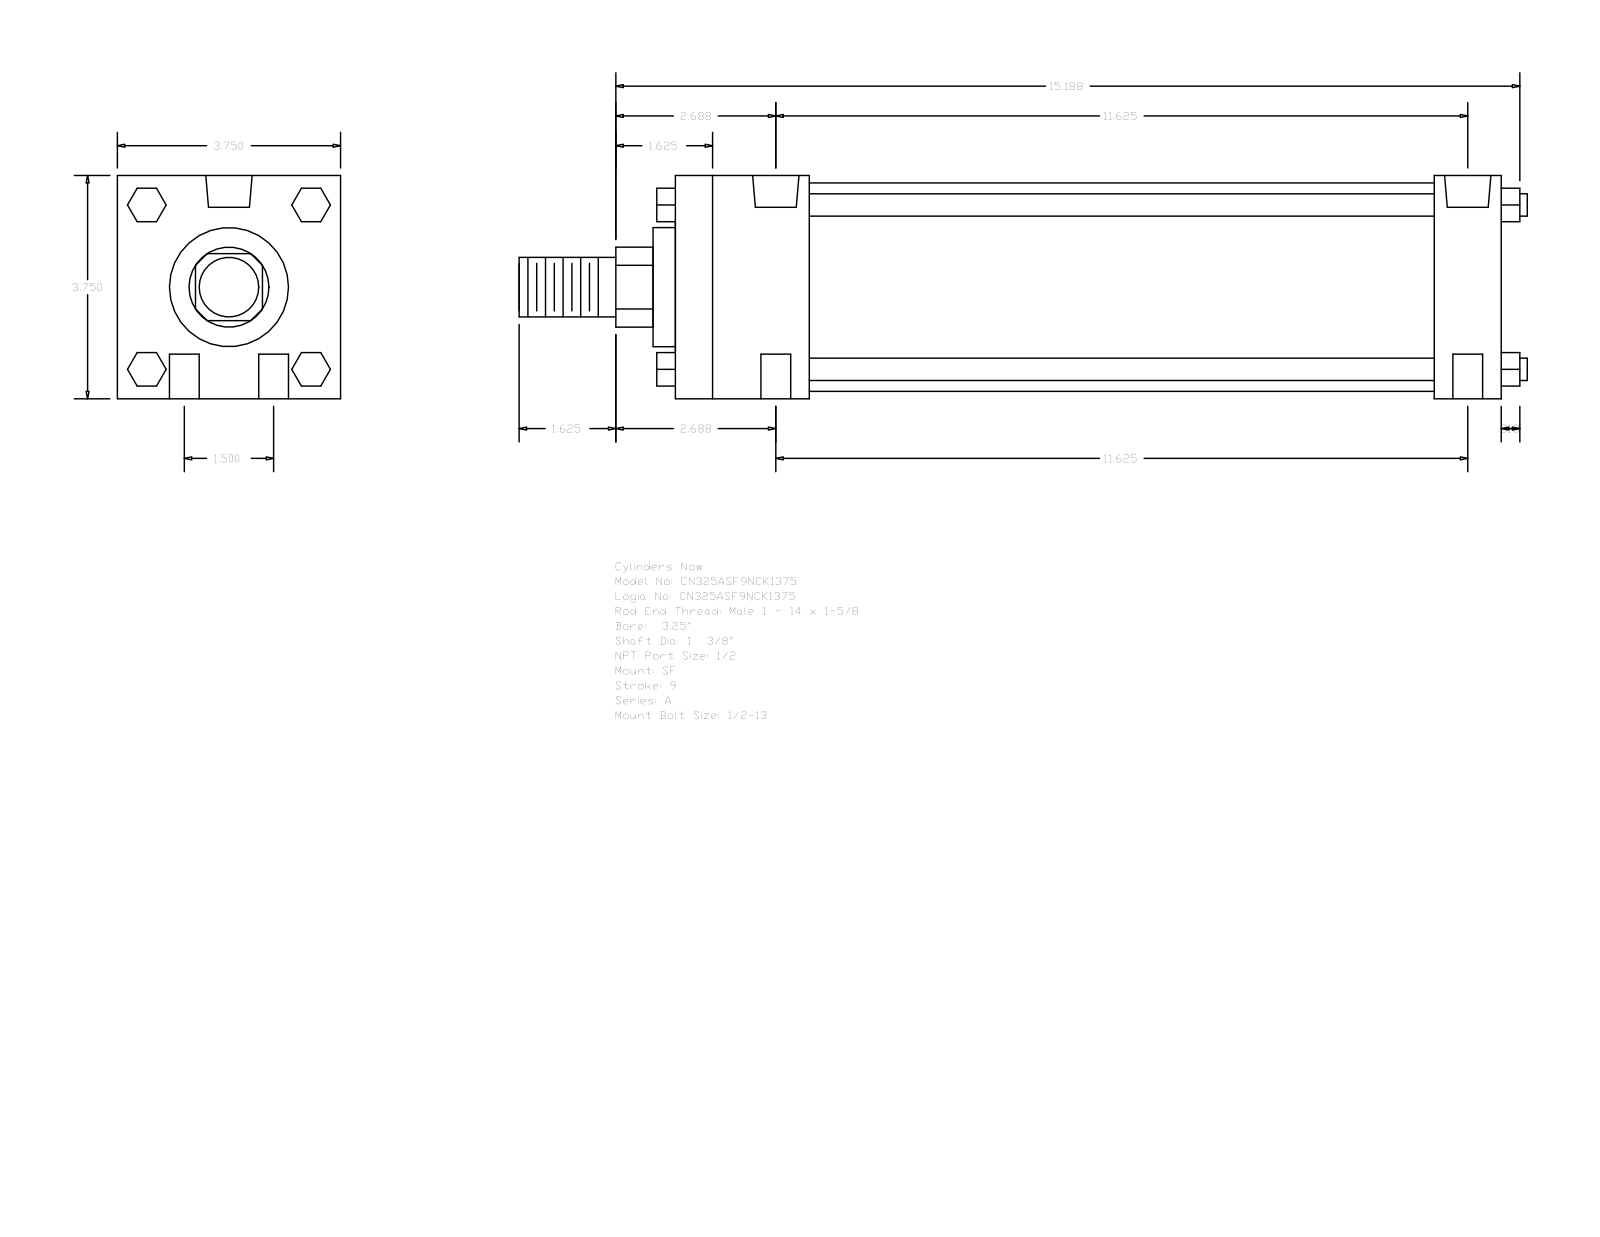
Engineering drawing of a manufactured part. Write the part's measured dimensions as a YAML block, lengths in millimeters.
part_name: "A_SF__0325_1.375"
step_written_by: "GSSL Pune (CONFIG_CONTROL_DESIGN)"
units: millimeters
bodies: {solids: 0, faces: 124, planar: 94, cylindrical: 30, other: 0}
overall_size: [430.21, 95.25, 95.25]
round_holes:
  - {diameter: 12.7, count: 4}
  - {diameter: 8.73, count: 2}
  - {diameter: 19.77, count: 2}
round_bosses_or_shafts:
  - {diameter: 9.53, count: 4}
  - {diameter: 88.9, count: 1}
  - {diameter: 50.8, count: 1}
  - {diameter: 34.92, count: 1}
  - {diameter: 25.4, count: 1}
partial_cylinders:
  - {radius: 17.06, count: 1}
face_to_face_distances: [95.24, 352.42, 57.15, 323.85, 28.57, 266.7, 295.27, 66.67, 9.52, 333.37]
hole_center_spacings: [19.05, 295.89, 295.28, 38.1, 297.73, 288.92]
